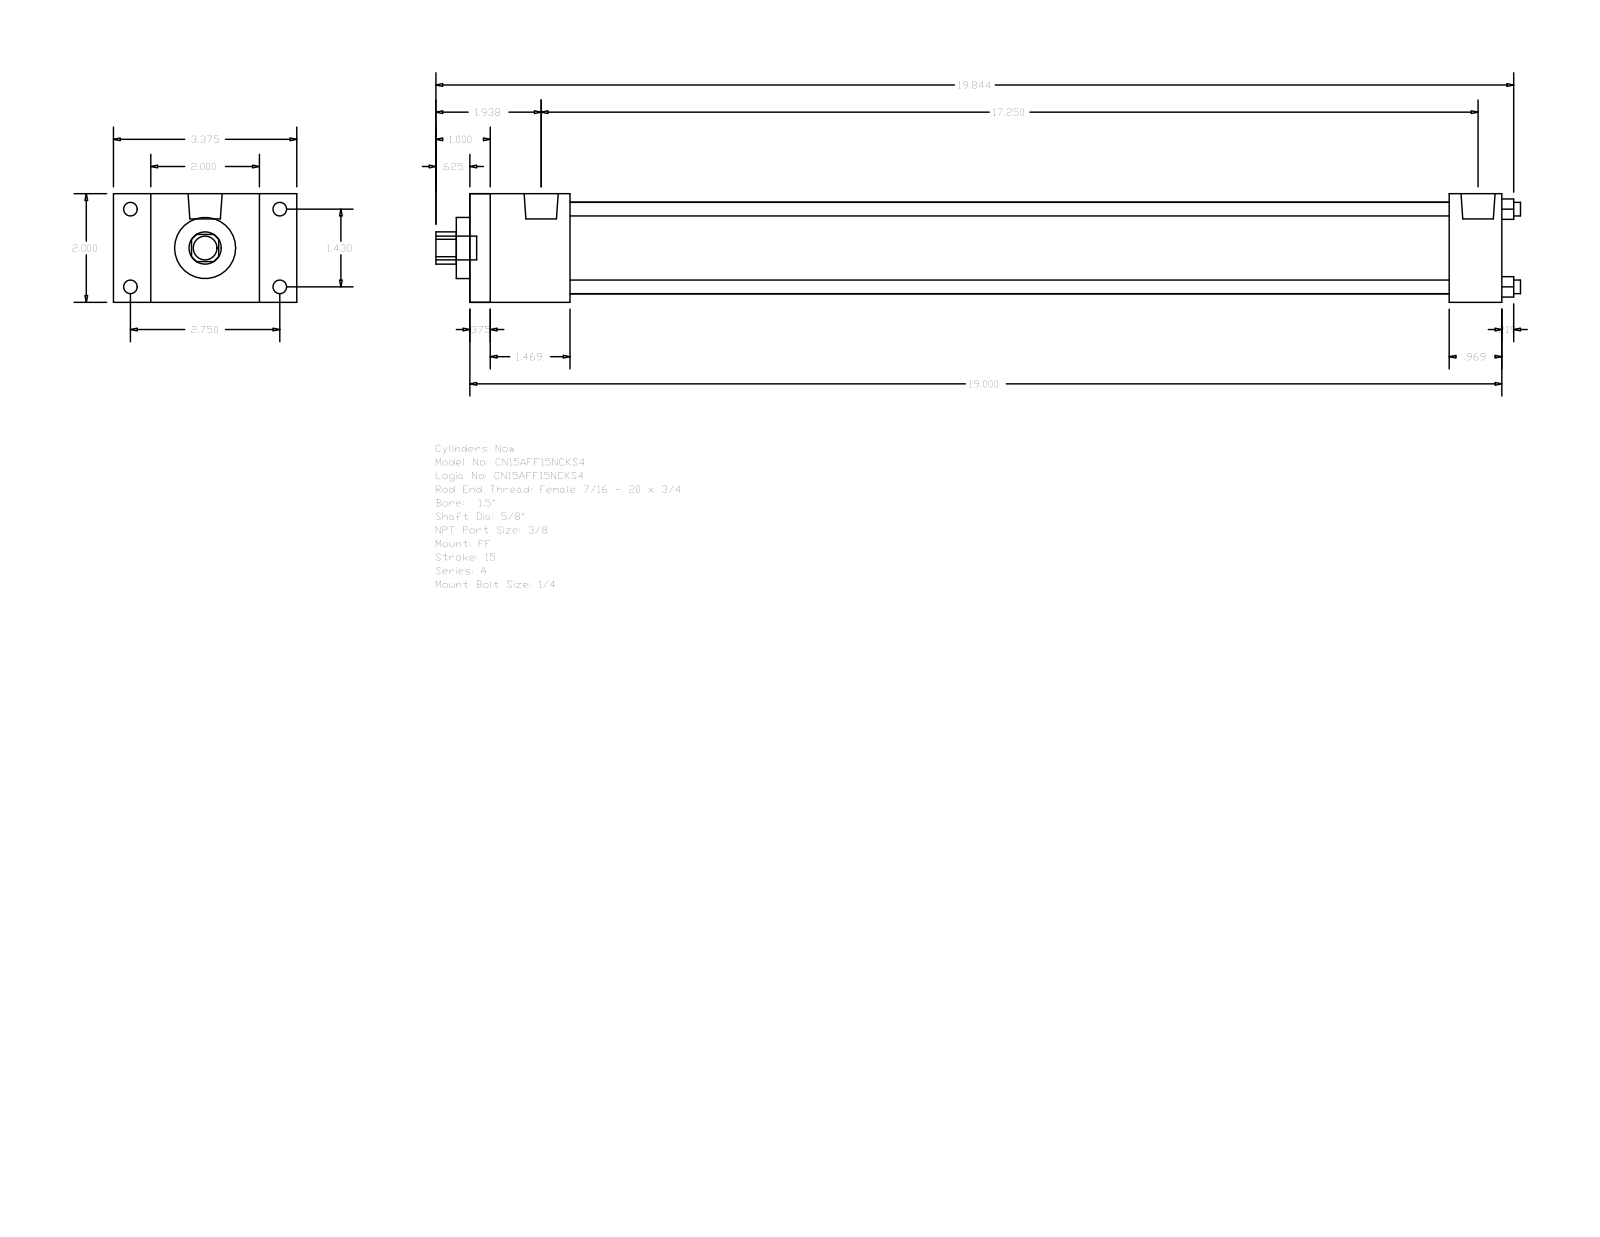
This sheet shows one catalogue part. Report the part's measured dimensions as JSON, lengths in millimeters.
{"part_name": "A_FF__0150_0.625", "step_written_by": "GSSL Pune (CONFIG_CONTROL_DESIGN)", "units": "millimeters", "bodies": {"solids": 0, "faces": 92, "planar": 64, "cylindrical": 28, "other": 0}, "overall_size": [507.21, 85.72, 50.8], "round_holes": [[6.35, 4], [15.88, 1], [28.57, 1], [42.93, 1]], "round_bosses_or_shafts": [[6.35, 4], [5.56, 4], [15.93, 2], [11.11, 1]], "partial_cylinders_radius": [[7.54, 1]], "face_to_face_distances": [50.8, 482.6, 9.52, 473.08, 46.83, 457.99, 37.31, 448.47, 411.16, 435.77], "hole_center_spacings": [25.68, 36.32, 51.36]}
